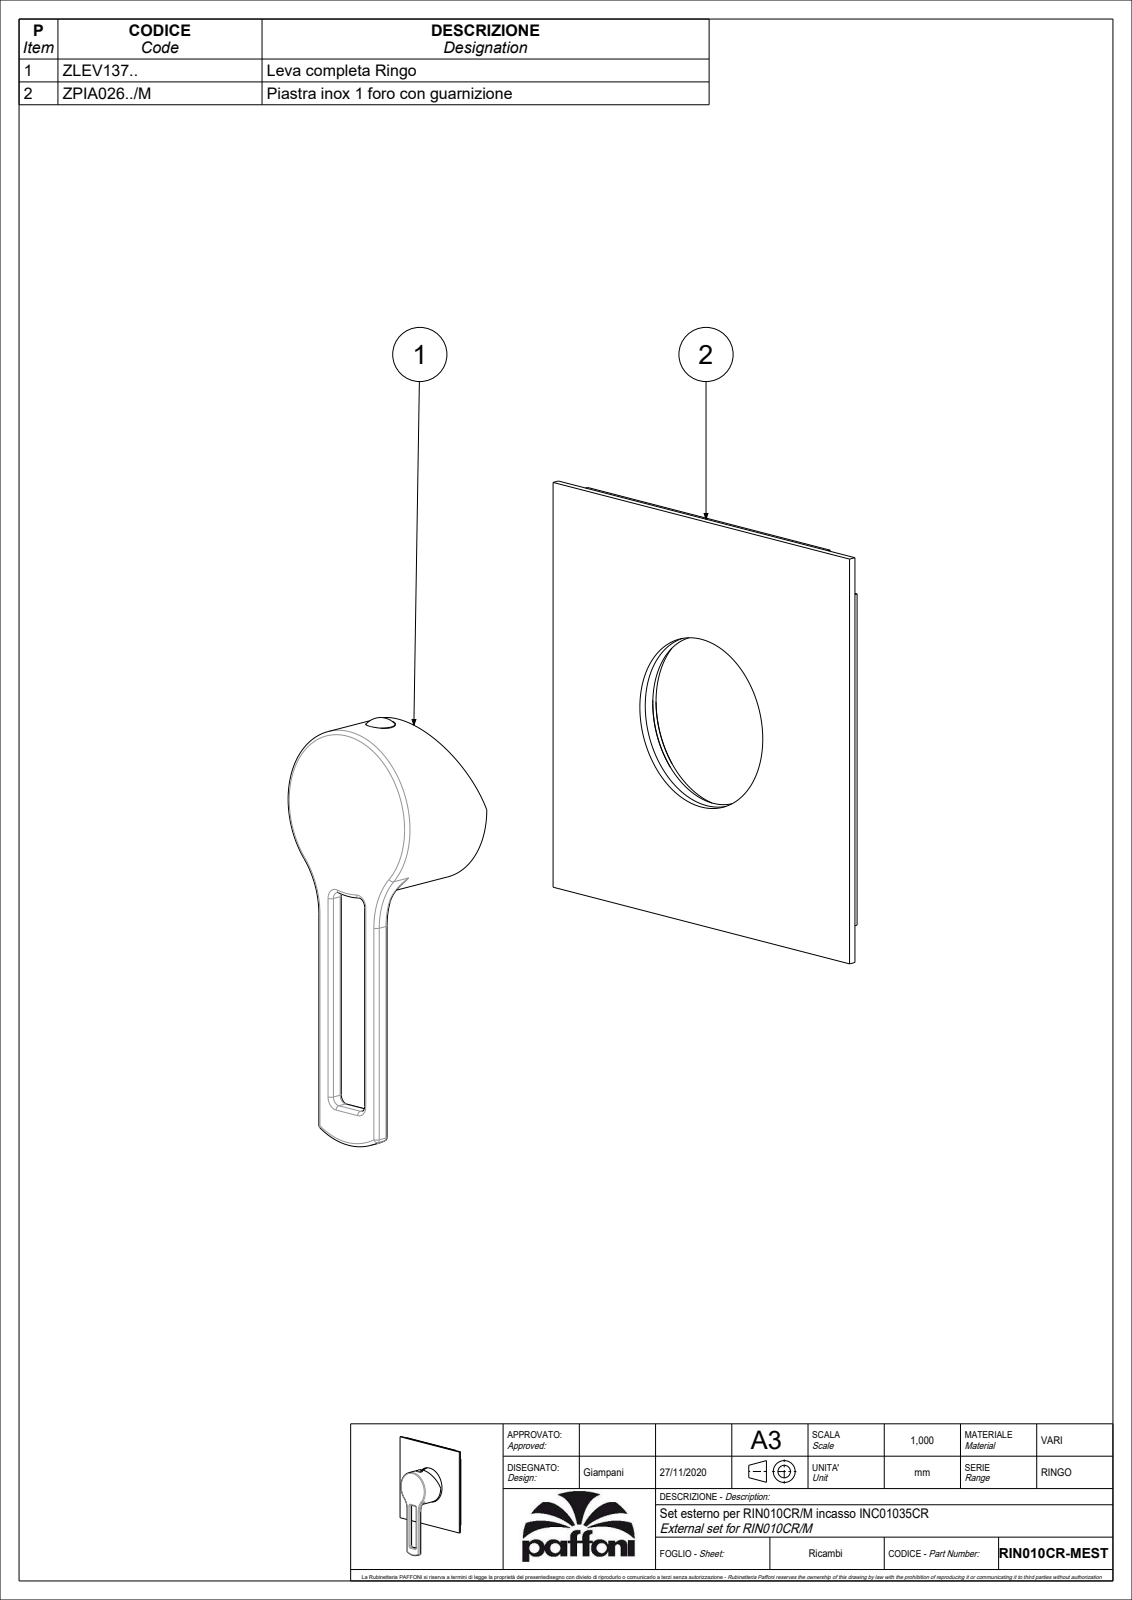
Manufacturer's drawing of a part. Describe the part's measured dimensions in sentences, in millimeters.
The part is named "RIN010CR-MEST". Its 3-D file was written by "CREO PARAMETRIC BY PTC INC, 2020044 (CONFIG_CONTROL_DESIGN)". It is 2 solids with 251 faces: 81 planar, 71 cylindrical and 99 other. Overall it measures 145 by 110 by 39 millimeters. Its volume is 43 959 cubic millimeters and its surface area 39 640 square millimeters. Round holes: 1 of diameter 3, 1 of diameter 7.8, 1 of diameter 45.6, 1 of diameter 47.6, 1 of diameter 51.1. Round bosses or shafts: 1 of diameter 54.6, 1 of diameter 44.8, 1 of diameter 7.6, 1 of diameter 5.5, 1 of diameter 5. Partial cylindrical surfaces (rounded edges, fillets, slot ends): 12 of radius 1, 8 of radius 0.5, 4 of radius 2, 2 of radius 20, 1 of radius 21.67. The main face-to-face distances are 2, 0.8, 2.8, 34.3, 33.5, 31.5, 30.8, 30, 28, 3.5.
